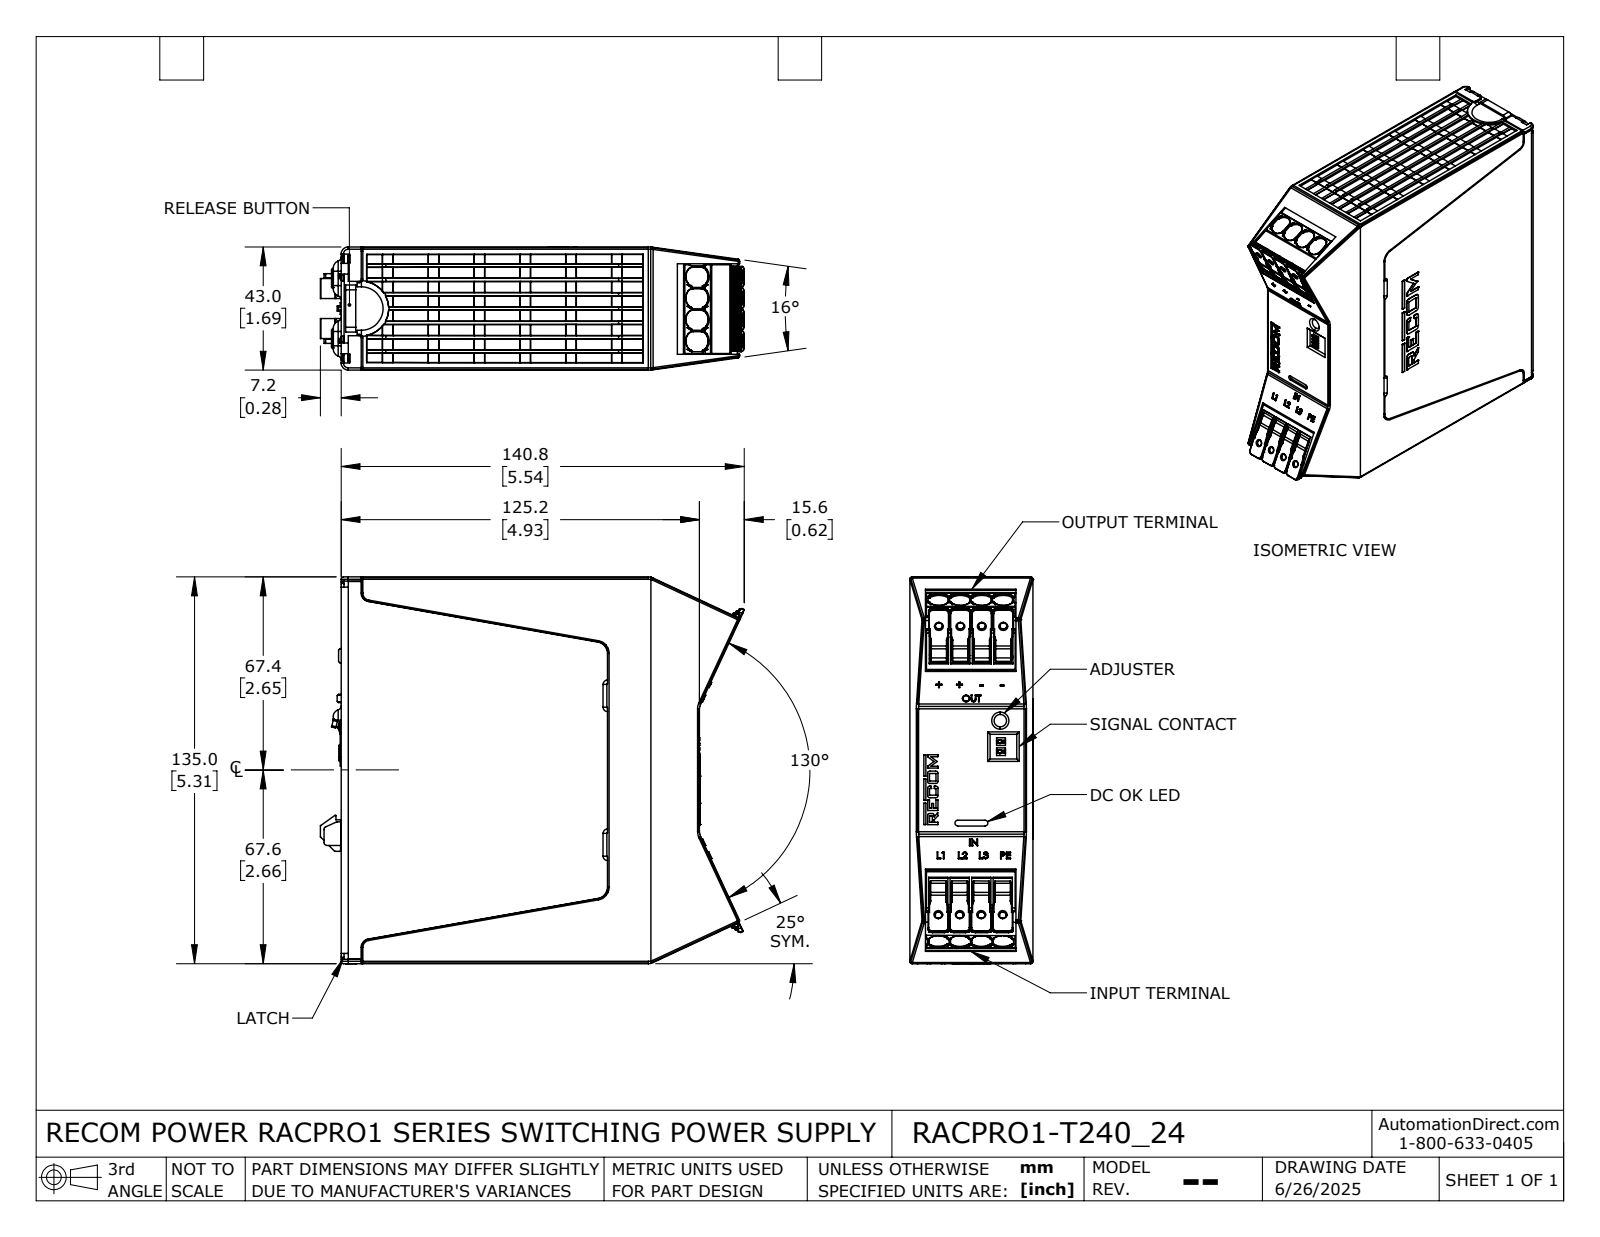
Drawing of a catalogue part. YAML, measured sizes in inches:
part_name: "RACPRO1-T240_24"
step_written_by: "SolidWorks 2024 (AUTOMOTIVE_DESIGN)"
units: inches
bodies: {solids: 1, faces: 3060, planar: 1416, cylindrical: 912, other: 732}
overall_size: [5.827, 5.316, 1.695]
volume: 44.48
surface_area: 128.2
round_holes:
  - {diameter: 0.098, count: 8}
partial_cylinders:
  - {radius: 0.008, count: 212}
  - {radius: 0.039, count: 57}
  - {radius: 0.098, count: 43}
  - {radius: 0.02, count: 38}
  - {radius: 0.118, count: 24}
  - {radius: 0.059, count: 22}
  - {radius: 0.031, count: 21}
  - {radius: 0.119, count: 20}
face_to_face_distances: [1.693, 0.059, 1.634, 5.268, 0.02, 5.295, 4.927, 5.315, 0.028, 5.287]
hole_center_spacings: [0.295, 0.591, 0.886]
